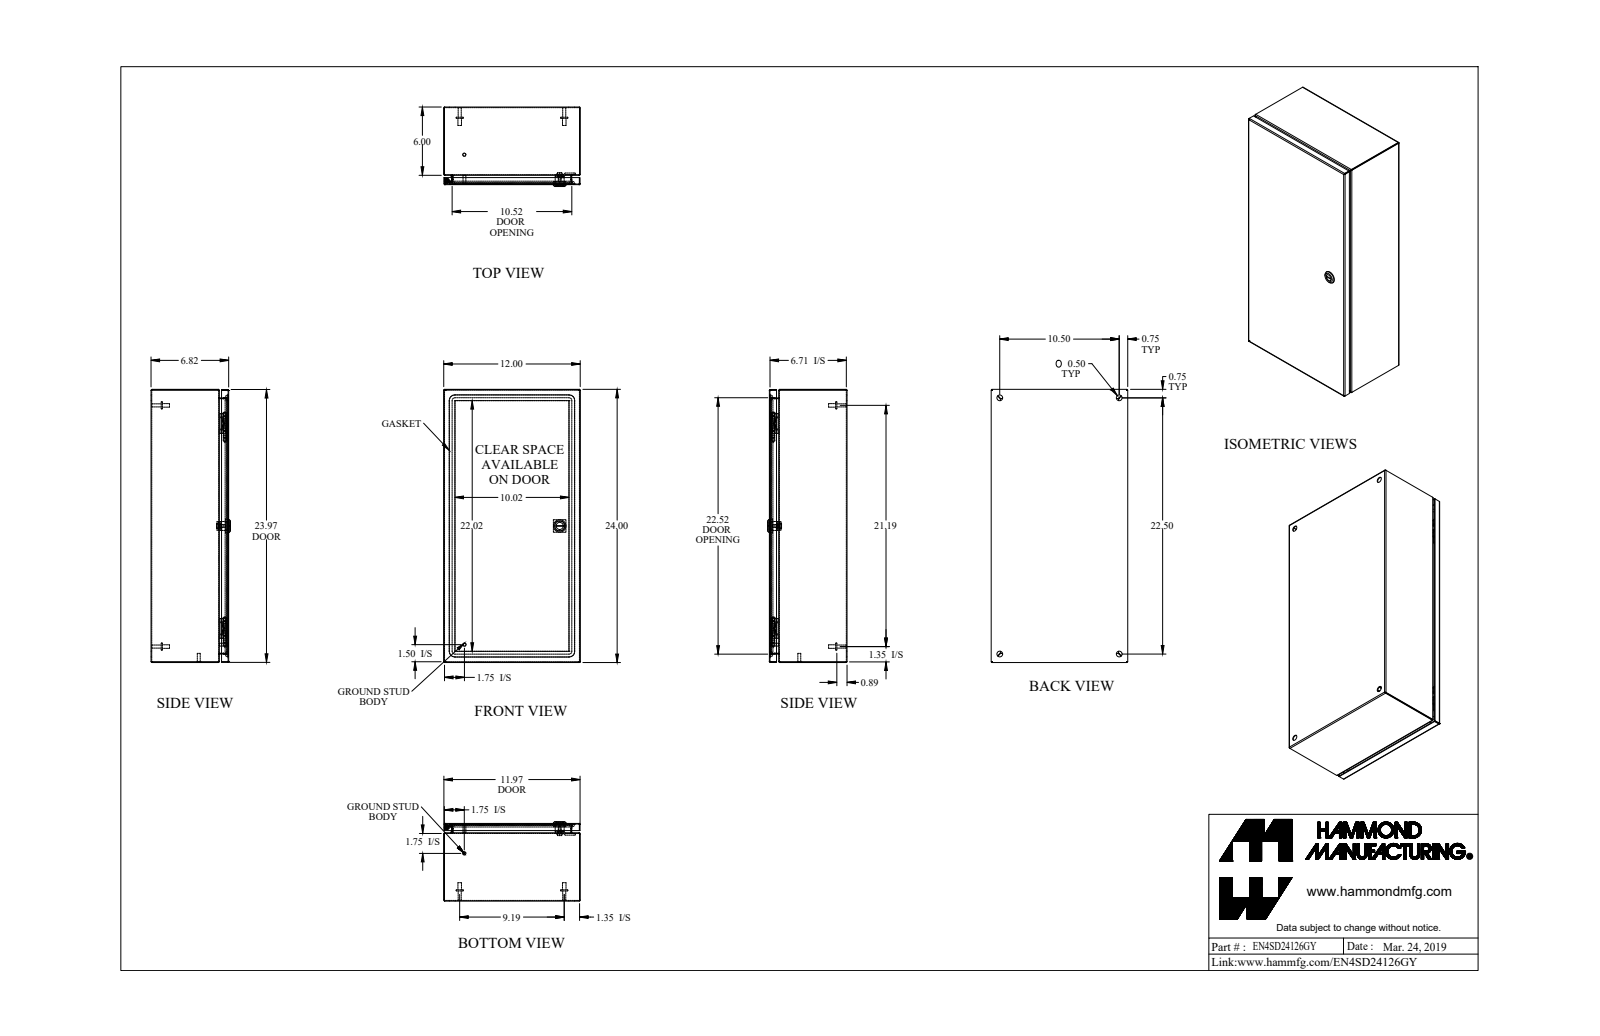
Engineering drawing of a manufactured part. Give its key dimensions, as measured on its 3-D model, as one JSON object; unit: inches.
{"part_name": "EN4SD24126GY_Default", "step_written_by": "SolidWorks 2019 (CONFIG_CONTROL_DESIGN)", "units": "inches", "bodies": {"solids": 21, "faces": 634, "planar": 285, "cylindrical": 213, "other": 136}, "overall_size": [24, 12, 6.982], "volume_in3": 72.64, "surface_area_in2": 2457, "round_holes": [[0.5, 4], [0.172, 1], [0.232, 1], [0.24, 1], [0.242, 1], [0.625, 1], [0.785, 1]], "round_bosses_or_shafts": [[0.625, 4], [0.313, 4], [0.27, 4], [0.281, 2], [0.25, 2], [1.1, 1], [0.525, 1], [0.455, 1]], "partial_cylinders_radius": [[0.029, 21], [0.086, 21], [0.25, 16], [19, 8], [0.006, 4], [0.062, 4], [0.499, 4], [0.125, 2]], "face_to_face_distances": [0.057, 6.765, 6.708, 6.822, 11.943, 11.886, 12, 23.943, 0.822, 5.943], "hole_center_spacings": [10.5, 22.5, 24.83, 11.299, 11.3, 14.686, 14.687]}
